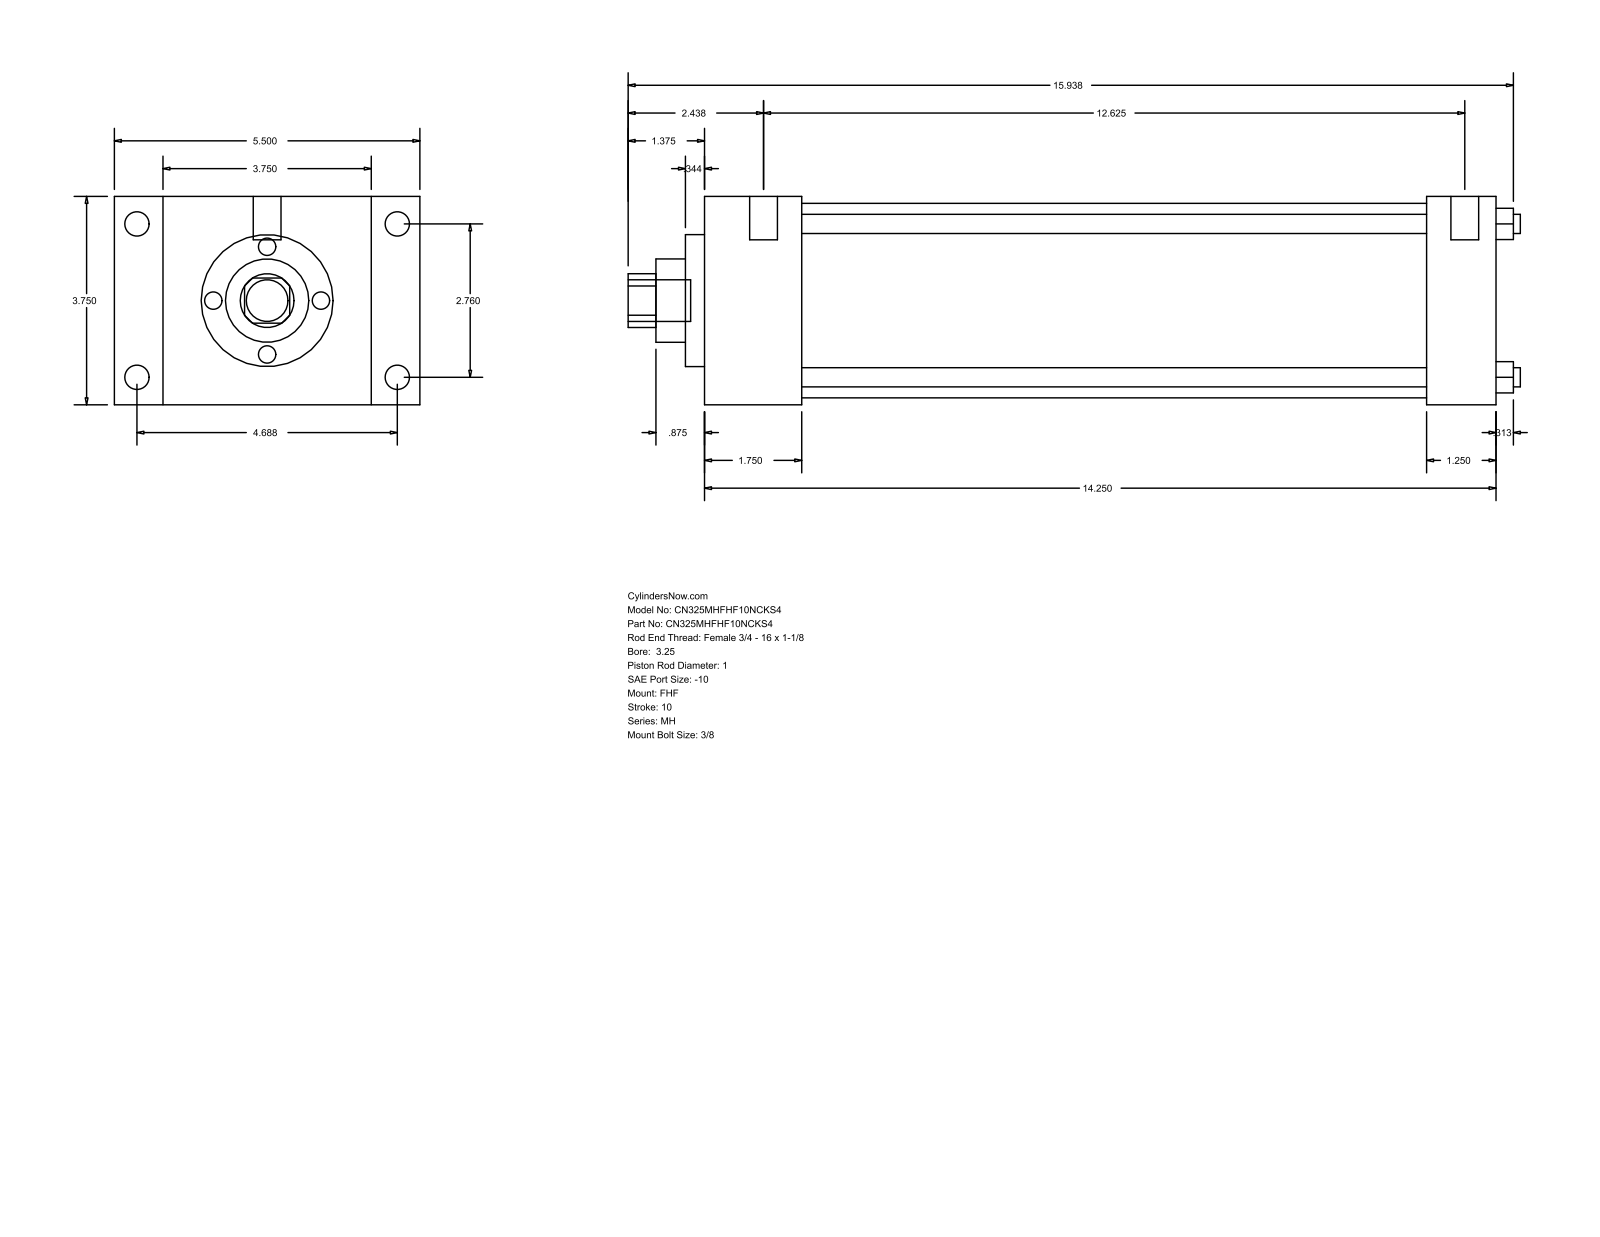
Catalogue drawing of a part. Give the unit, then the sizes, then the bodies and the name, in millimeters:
Units: millimetres
Overall size (bounding box): 407.99 × 139.7 × 95.25
Round holes (diameter × count): ⌀8.76 ×4, ⌀25.4 ×1, ⌀38.1 ×1, ⌀60.33 ×1, ⌀88.9 ×1
Round bosses / shafts (diameter × count): ⌀11.13 ×4, ⌀5.56 ×4, ⌀12.7 ×2, ⌀19.05 ×1
Partial cylindrical surfaces — rounded edges, fillets, slot ends (radius × count): R12.29 ×1
Main face-to-face distances: 95.24, 361.96, 44.46, 317.5, 22.23, 117.47, 139.7, 330.2, 285.74, 31.76
Hole centre spacings: 49.57, 70.1, 99.14
Bodies: 0 solids, 90 faces (61 planar, 29 cylindrical, 0 other)
Part name (STEP PRODUCT): MH_FHF__0325_1
STEP written by: GSSL Pune (CONFIG_CONTROL_DESIGN)
